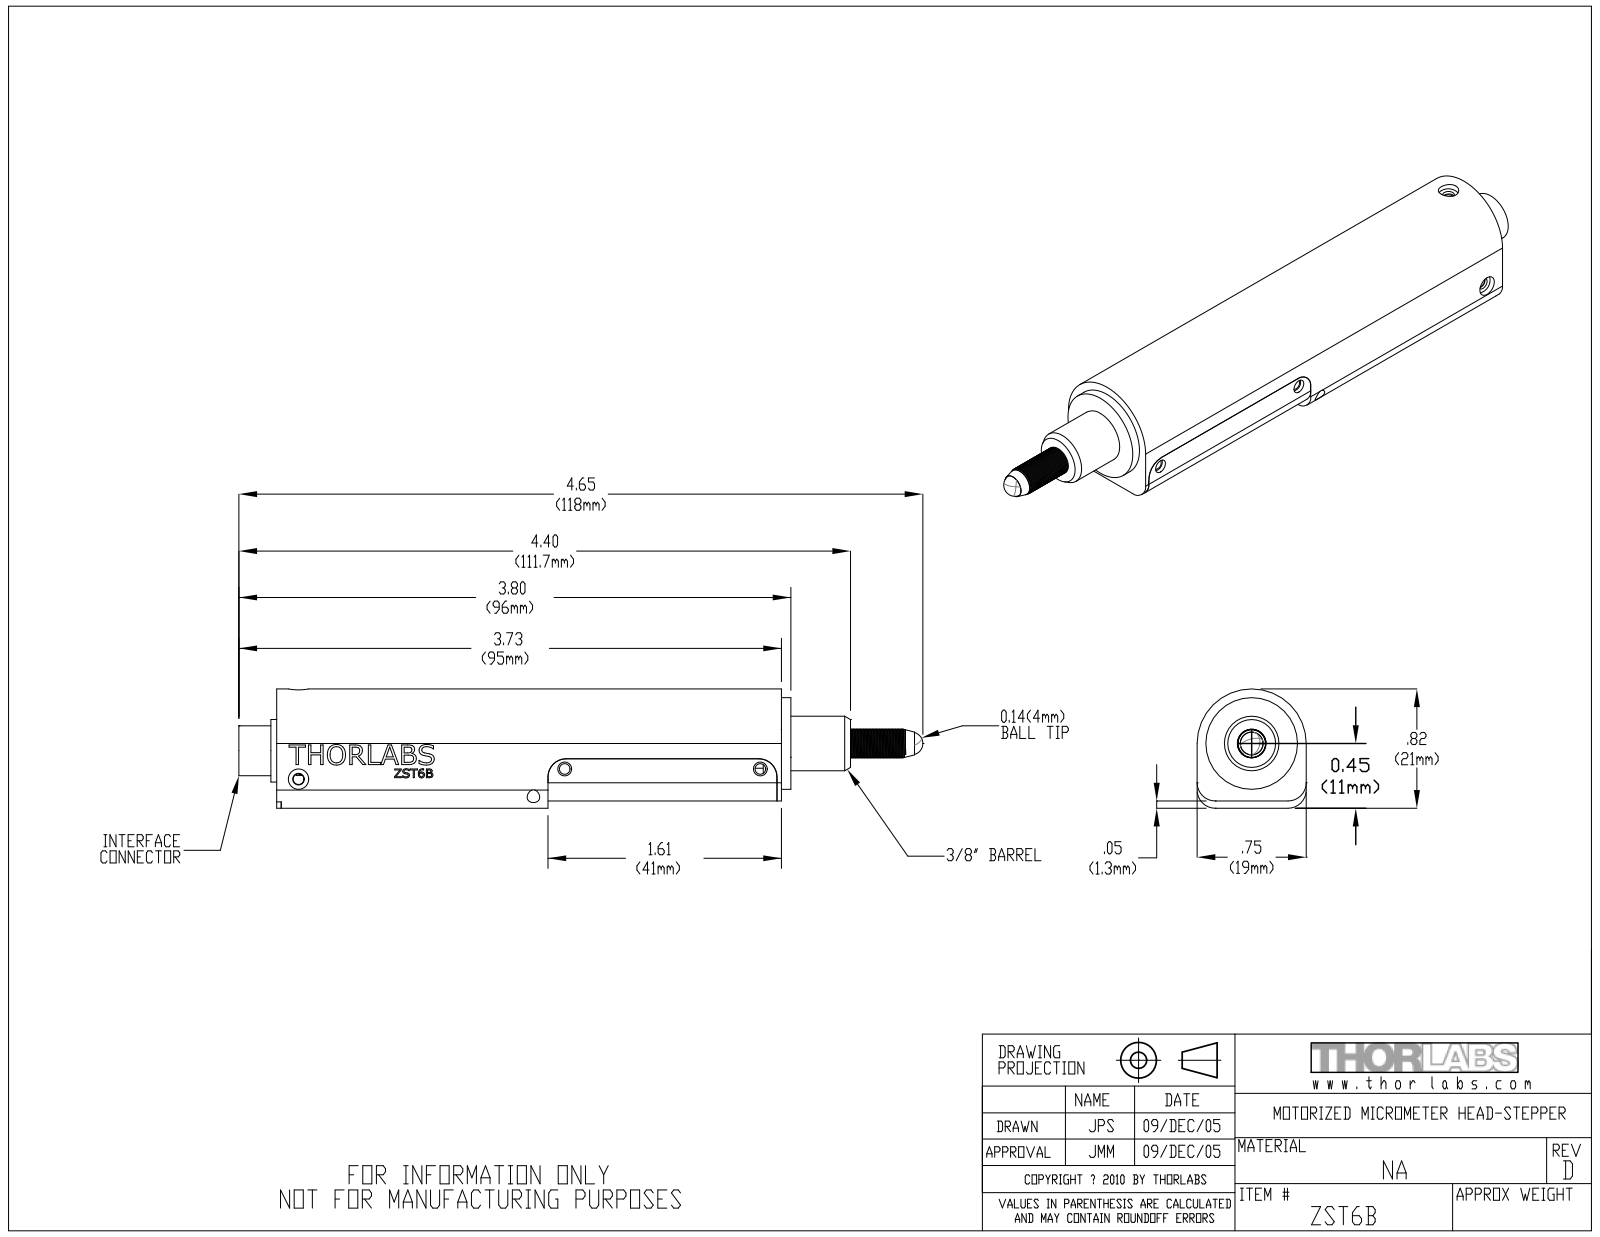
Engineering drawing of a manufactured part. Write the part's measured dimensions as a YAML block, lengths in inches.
part_name: "12550-E0W"
step_written_by: "SolidWorks 2007 (AUTOMOTIVE_DESIGN)"
units: inches
bodies: {solids: 0, faces: 455, planar: 136, cylindrical: 268, other: 51}
overall_size: [4.702, 0.828, 0.82]
round_holes:
  - {diameter: 0.045, count: 7}
  - {diameter: 0.045, count: 3}
  - {diameter: 0.086, count: 2}
  - {diameter: 0.14, count: 2}
  - {diameter: 0.156, count: 1}
  - {diameter: 0.386, count: 1}
round_bosses_or_shafts:
  - {diameter: 0.139, count: 4}
  - {diameter: 0.073, count: 2}
  - {diameter: 0.63, count: 1}
  - {diameter: 0.551, count: 1}
  - {diameter: 0.464, count: 1}
  - {diameter: 0.375, count: 1}
  - {diameter: 0.3, count: 1}
  - {diameter: 0.197, count: 1}
partial_cylinders:
  - {radius: 0.125, count: 8}
  - {radius: 0.03, count: 3}
  - {radius: 0.345, count: 1}
  - {radius: 0.375, count: 1}
face_to_face_distances: [0.75, 0.05, 0.03, 3.44, 3.47, 3.535, 3.505, 0.065, 0.26, 0.29]
hole_center_spacings: [0.071, 0.14, 0.1, 0.103, 0.108, 0.128, 0.158, 0.199]
